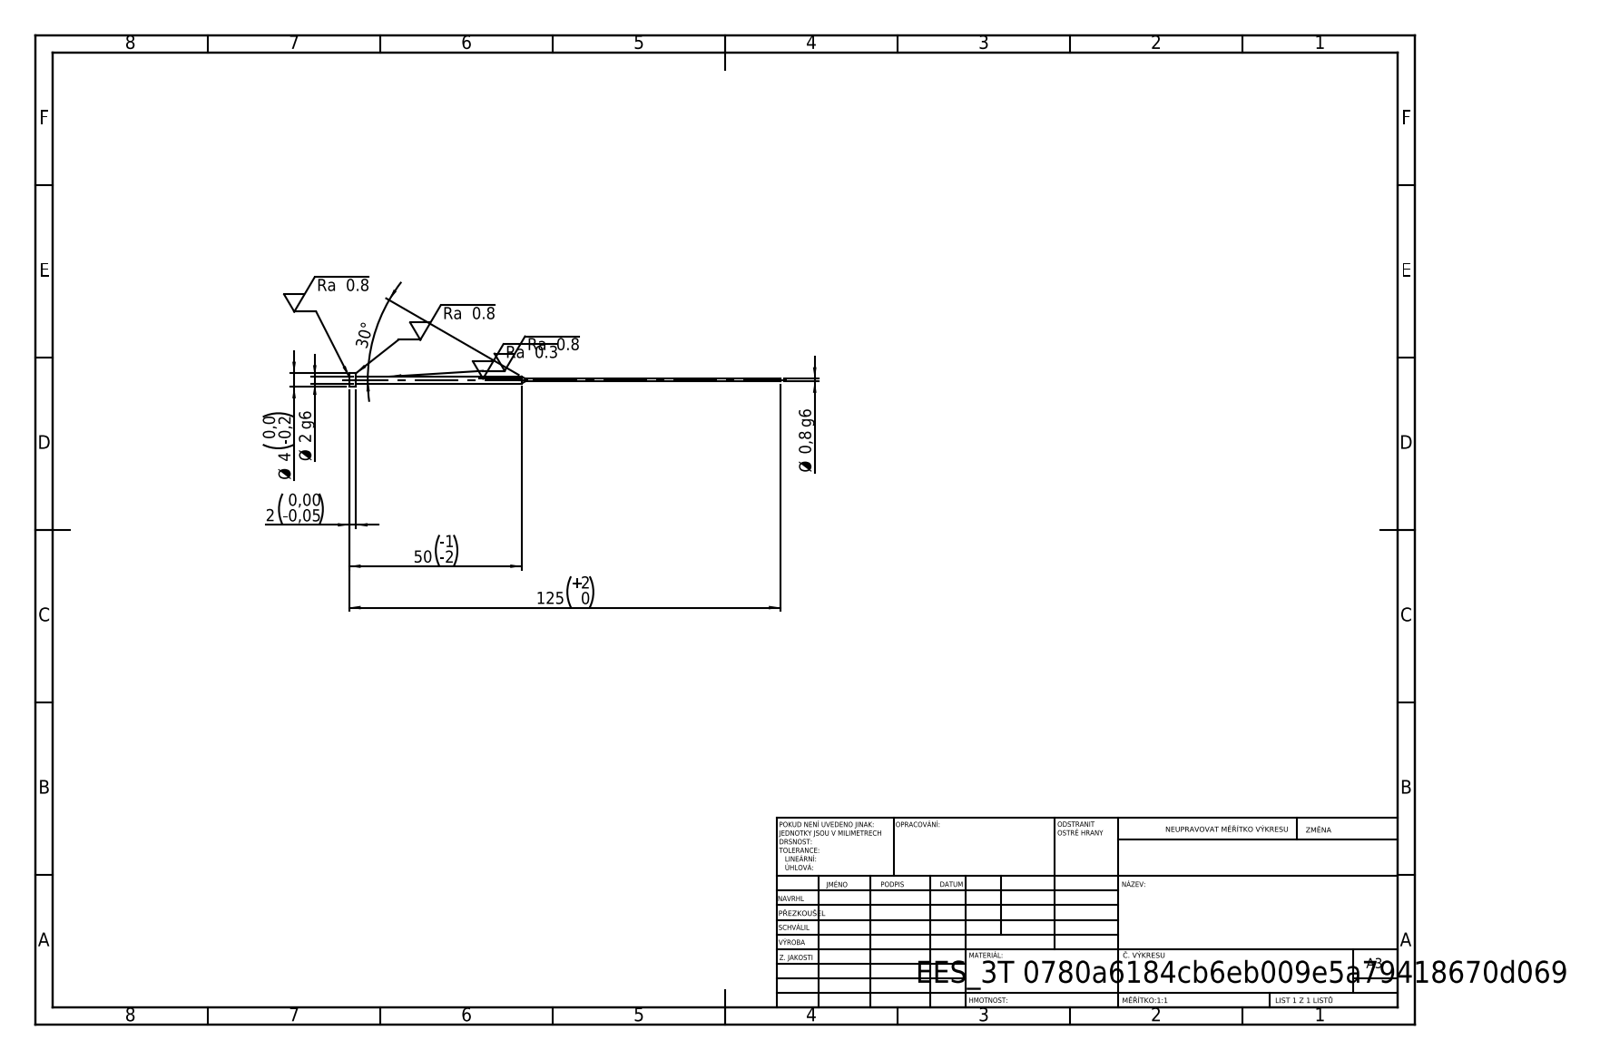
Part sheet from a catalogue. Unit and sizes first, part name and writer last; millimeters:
Units: millimetres
Overall size (bounding box): 125 × 4 × 4
Round bosses / shafts (diameter × count): ⌀4 ×1, ⌀2 ×1, ⌀0.8 ×1
Main face-to-face distances: 2, 123, 125
Volume: 215 mm³ · Surface area: 540 mm²
Bodies: 1 solid, 11 faces (3 planar, 6 cylindrical, 2 other)
STEP written by: SolidWorks 2019 (CONFIG_CONTROL_DESIGN)
